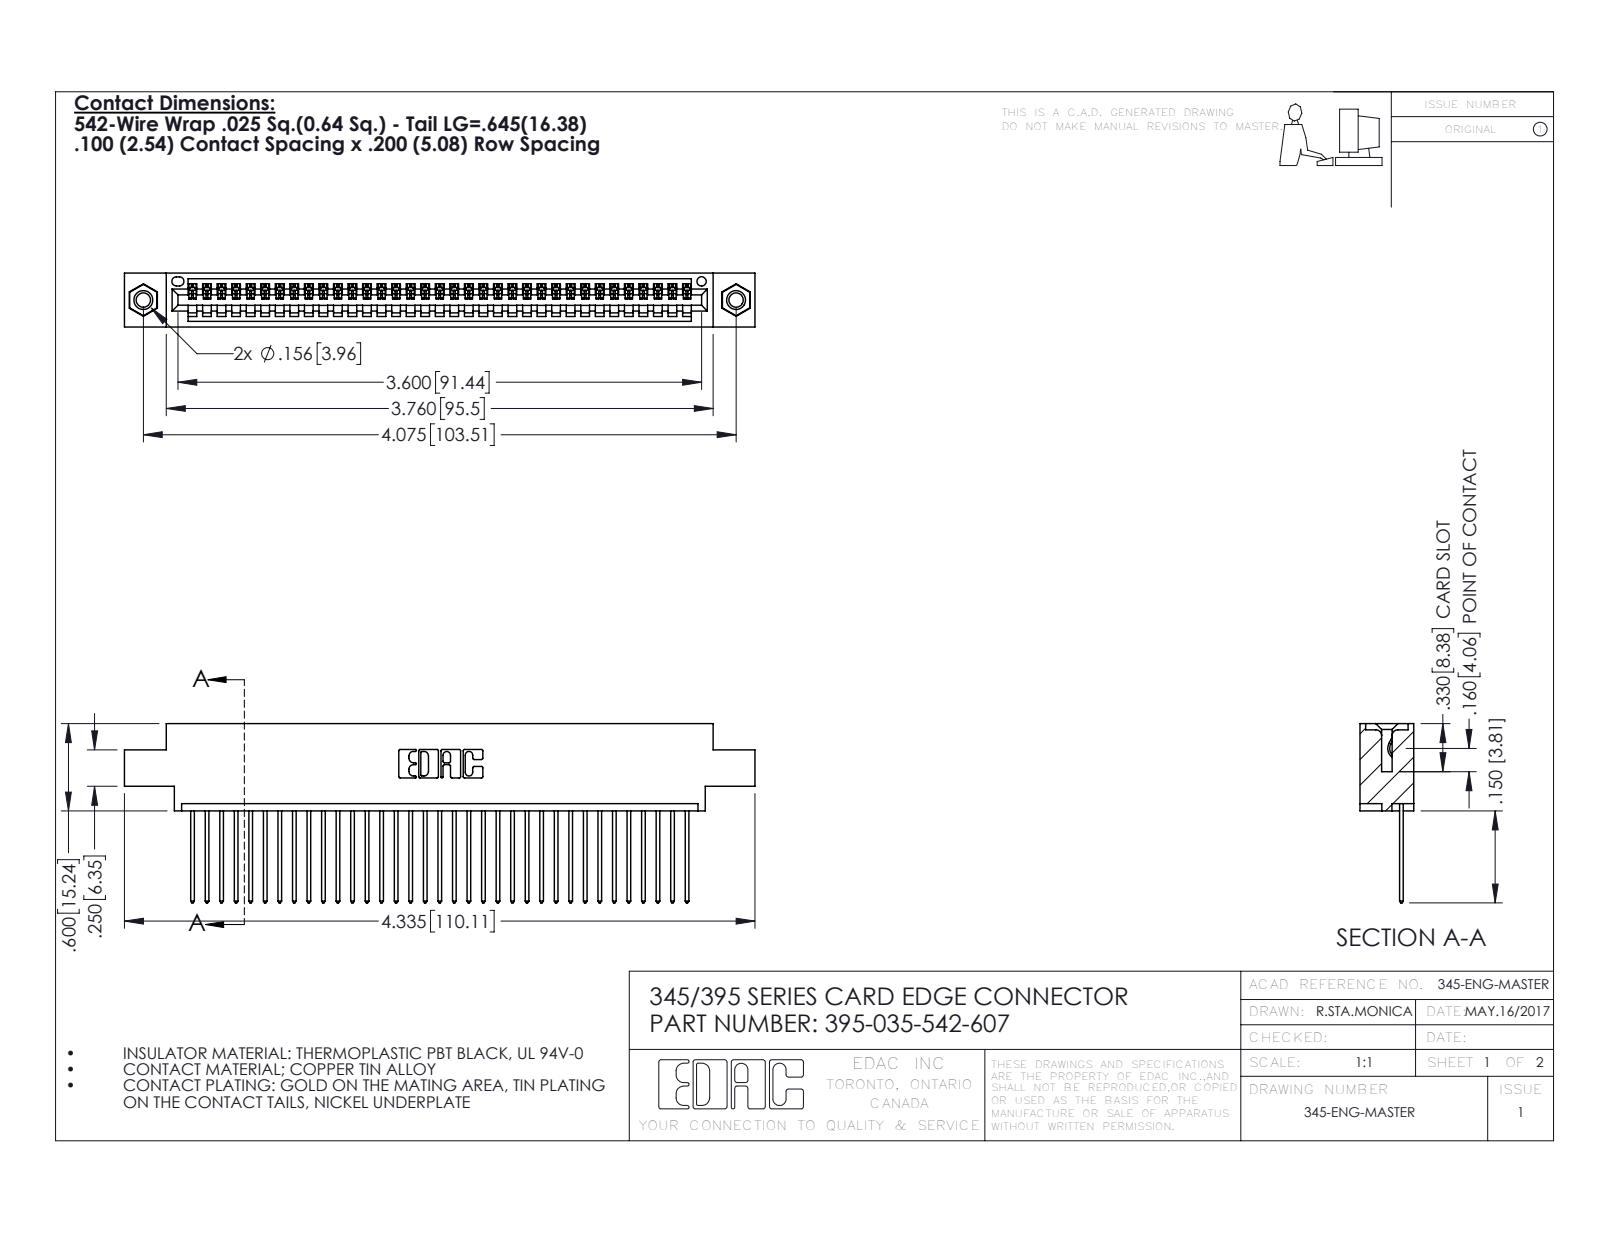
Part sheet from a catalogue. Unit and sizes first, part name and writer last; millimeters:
Units: millimetres
Overall size (bounding box): 110.1 × 31.3 × 9.4
Round holes (diameter × count): ⌀2.5 ×2, ⌀3.2 ×2, ⌀4 ×2, ⌀1.6 ×1
Round bosses / shafts (diameter × count): ⌀3.9 ×2
Partial cylindrical surfaces — rounded edges, fillets, slot ends (radius × count): R0.2 ×70, R0.3 ×70, R0.3 ×22, R0.2 ×6, R0.8 ×6, R0.7 ×3, R0.8 ×2, R1 ×2
Main face-to-face distances: 1.8, 7.6, 9.4, 2.5, 6.9, 0.6, 5.1, 5.7, 4.4, 3.8
Hole centre spacings: 6.9, 97.5, 103.5
Volume: 10 400 mm³ · Surface area: 14 320 mm²
Bodies: 38 solids, 2220 faces (1516 planar, 688 cylindrical, 16 other)
Part name (STEP PRODUCT): 345-250-001_345-250-005-103; 345-292-001_345-293-142; 345 Part_0.170 Offset - 0.156 Dia-TI; 395-035-542-607
STEP written by: SolidWorks 2016 (CONFIG_CONTROL_DESIGN)
